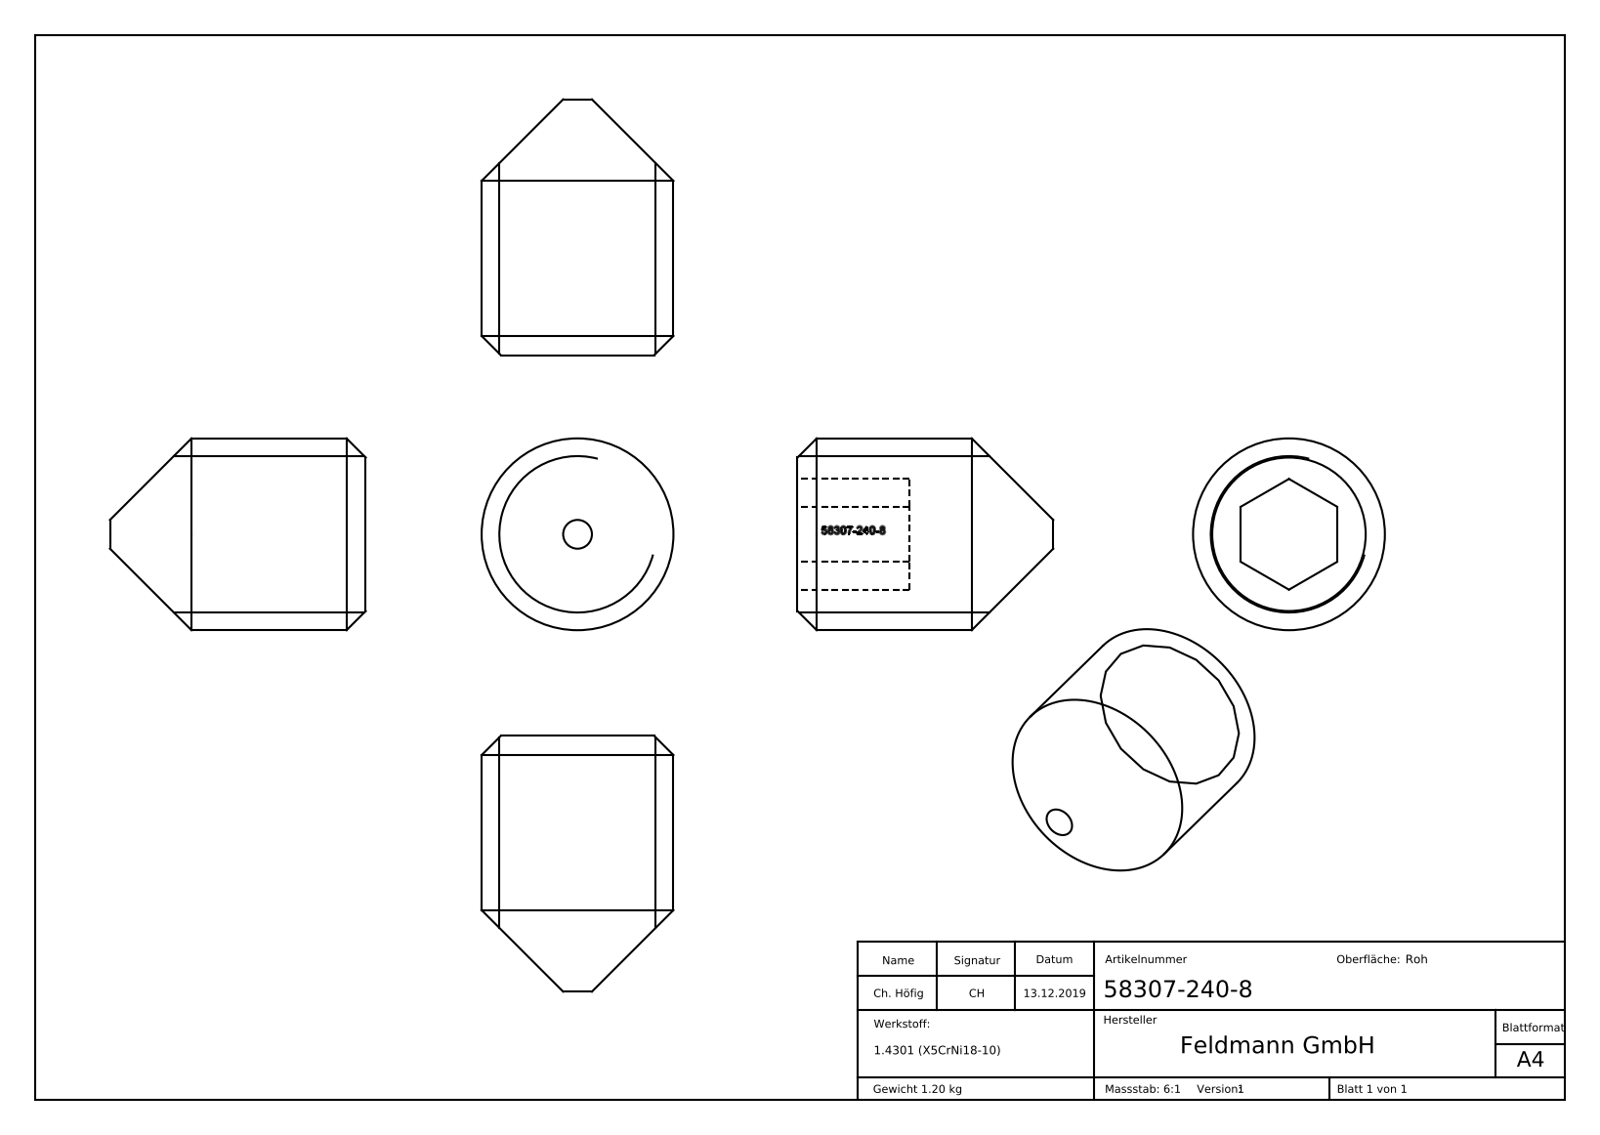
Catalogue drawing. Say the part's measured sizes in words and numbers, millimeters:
The part is named "58307-240-8". Its 3-D file was written by "SolidWorks 2015 (CONFIG_CONTROL_DESIGN)". It is 1 solid with 158 faces: 68 planar, 1 cylindrical and 89 other. Overall it measures 70 by 6 by 6 millimeters. Its volume is 152 cubic millimeters and its surface area 201 square millimeters. Round bosses or shafts: 1 of diameter 6. The main face-to-face distances are 3, 3.5, 4.5, 8, 3.1, 5.81, 1.31, 2.19, 5.84, 1.34.
